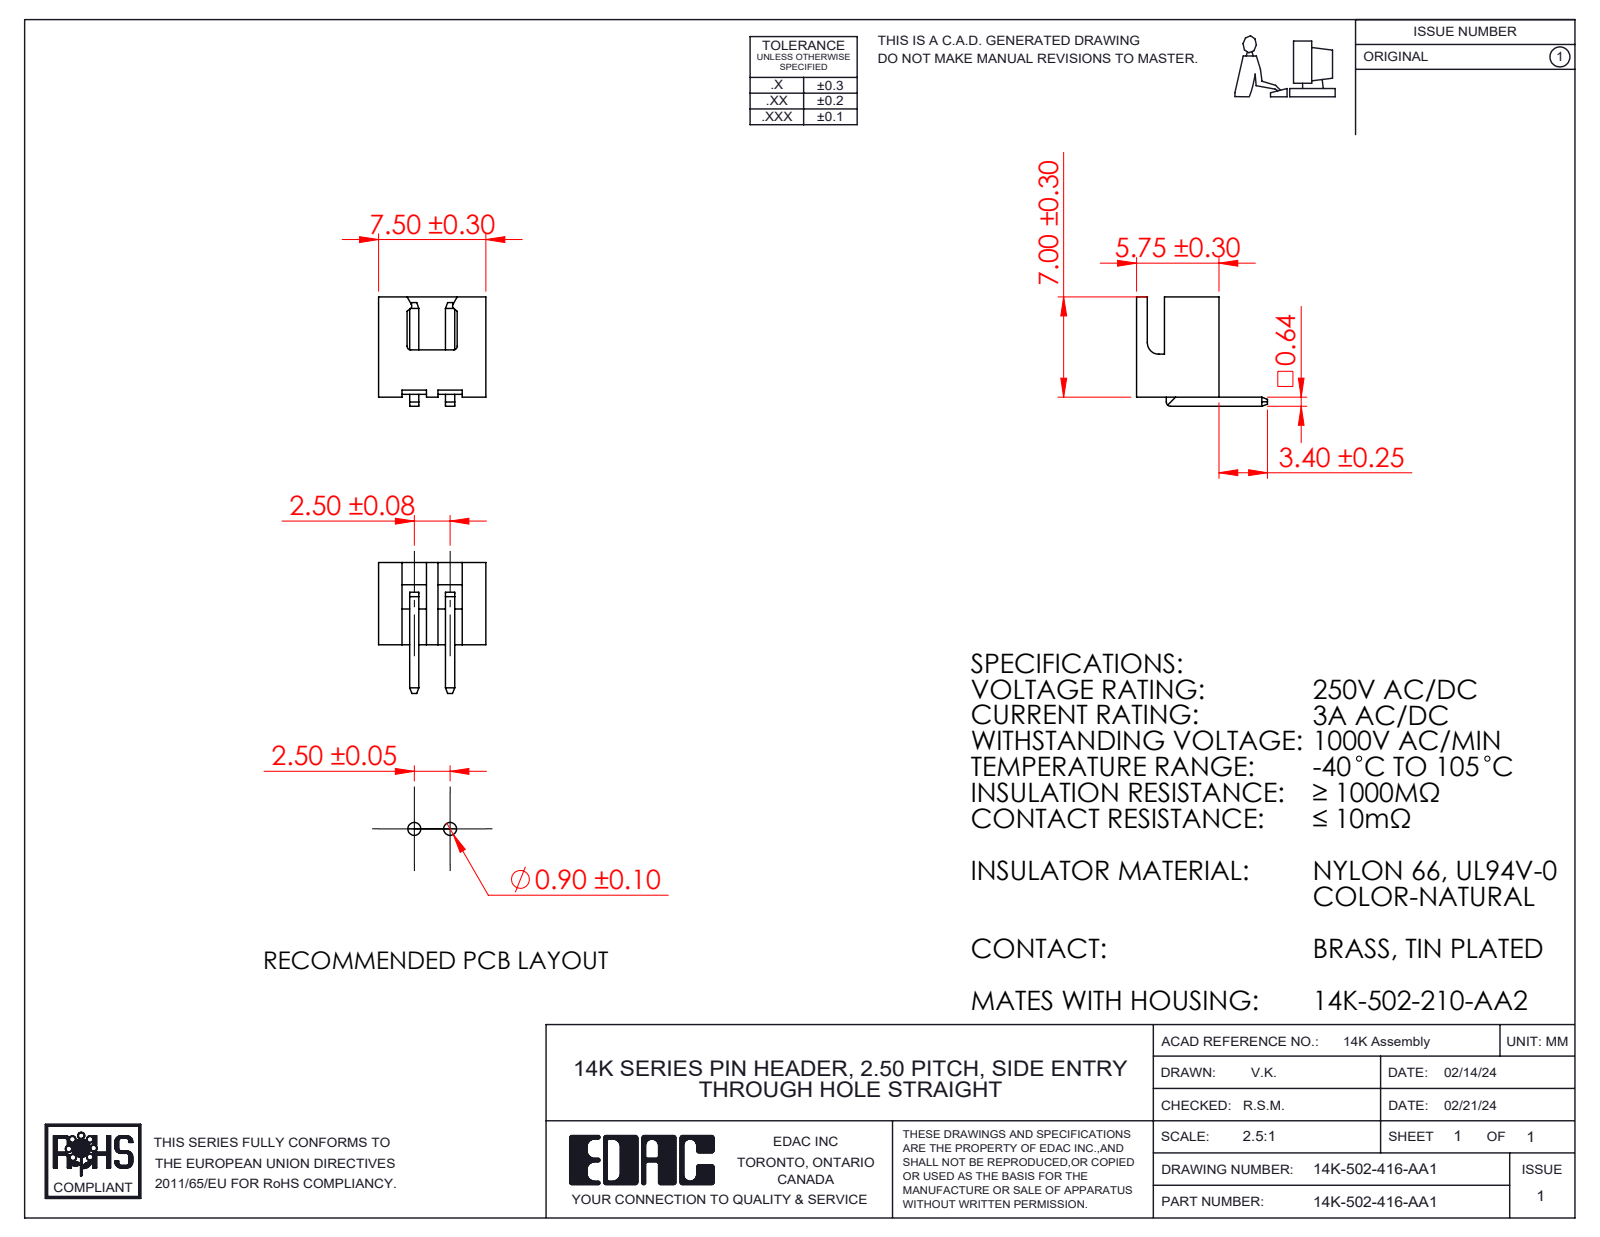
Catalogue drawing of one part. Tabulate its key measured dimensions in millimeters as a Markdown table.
| quantity | value |
| --- | --- |
| part name | 14K Series Pin_16; 14K-502-416-AA1; 14K Series Pin Header Insulator_502 |
| STEP written by | SolidWorks 2023 (CONFIG_CONTROL_DESIGN) |
| units | millimeters |
| bodies | 3 solids, 98 faces (87 planar, 11 cylindrical, 0 other) |
| overall size | 9.15 × 7.64 × 7.5 |
| volume | 155 mm³ |
| surface area | 434 mm² |
| partial cylindrical surfaces (radius × count) | 0.25 × 4, 0.3 × 2, 0.8 × 1 |
| main face-to-face distances | 0.76, 5, 5.76, 7.5, 0.75, 6.75, 0.64, 2.5, 4.24, 2.18 |
